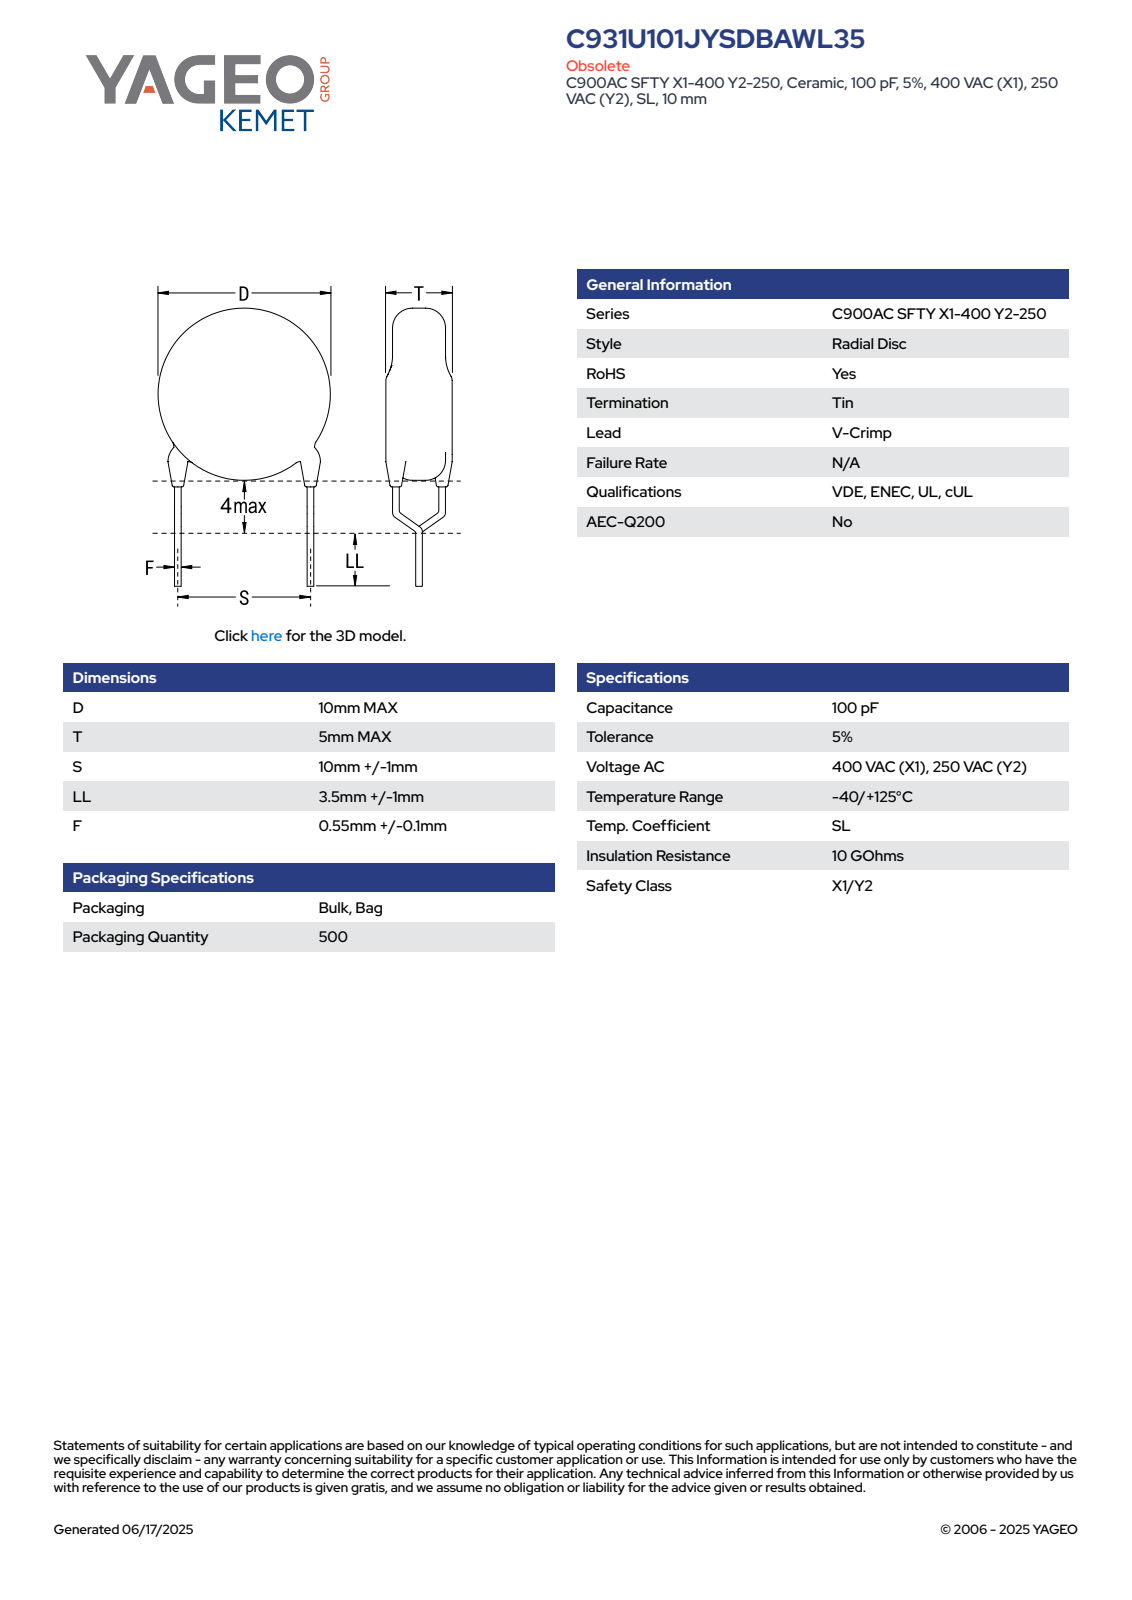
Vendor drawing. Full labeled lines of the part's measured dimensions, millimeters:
Part name (STEP PRODUCT): CCD_VCC900_D10T5S10LL4.5F0.65
STEP written by: SolidWorks 2014 (AUTOMOTIVE_DESIGN)
Units: millimetres
Bodies: 5 solids, 93 faces (65 planar, 16 cylindrical, 12 other)
Overall size (bounding box): 18.3 × 10.65 × 5
Volume: 390 mm³ · Surface area: 346 mm²
Round bosses / shafts (diameter × count): ⌀0.65 ×6, ⌀10 ×1
Main face-to-face distances: 5, 7.4, 1.3, 13.95, 6.55, 12.65, 5.25, 0.32, 1.05, 2.68
